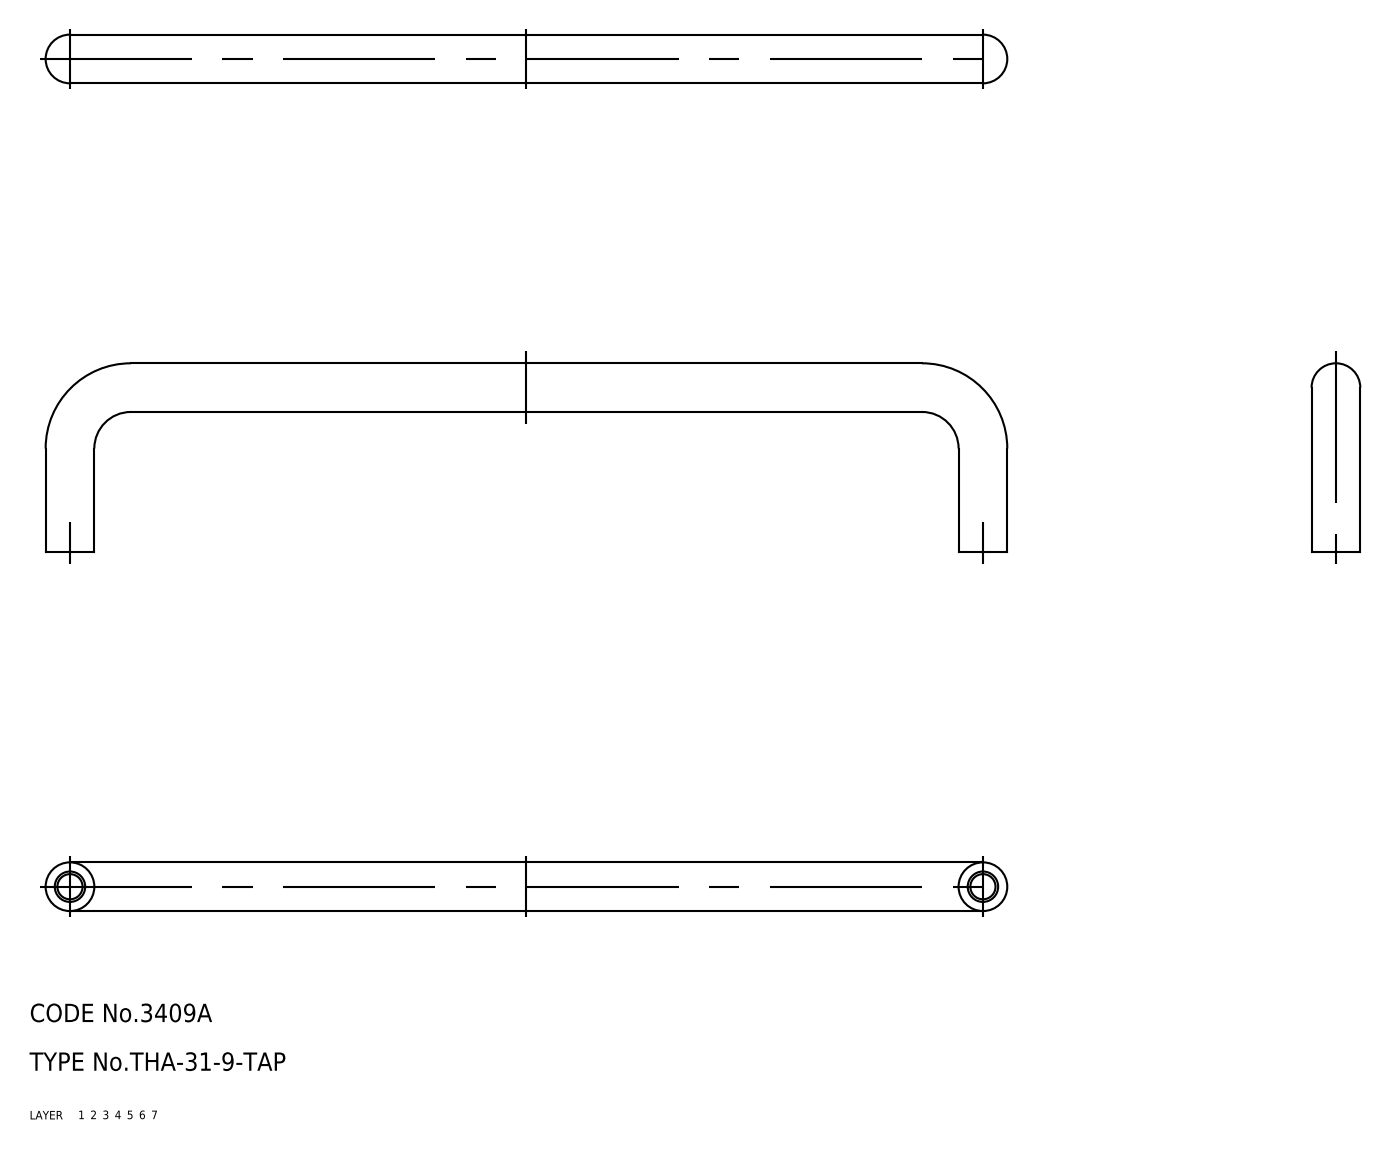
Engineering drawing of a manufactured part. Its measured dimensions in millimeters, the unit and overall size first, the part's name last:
Units: millimetres
Overall size (bounding box): 158 × 31 × 8
Volume: 9 351 mm³ · Surface area: 5 424 mm²
Bodies: 1 solid, 18 faces (0 planar, 0 cylindrical, 18 other)
Part name (STEP PRODUCT): pull
STEP written by: CADfix (AUTOMOTIVE_DESIGN)
